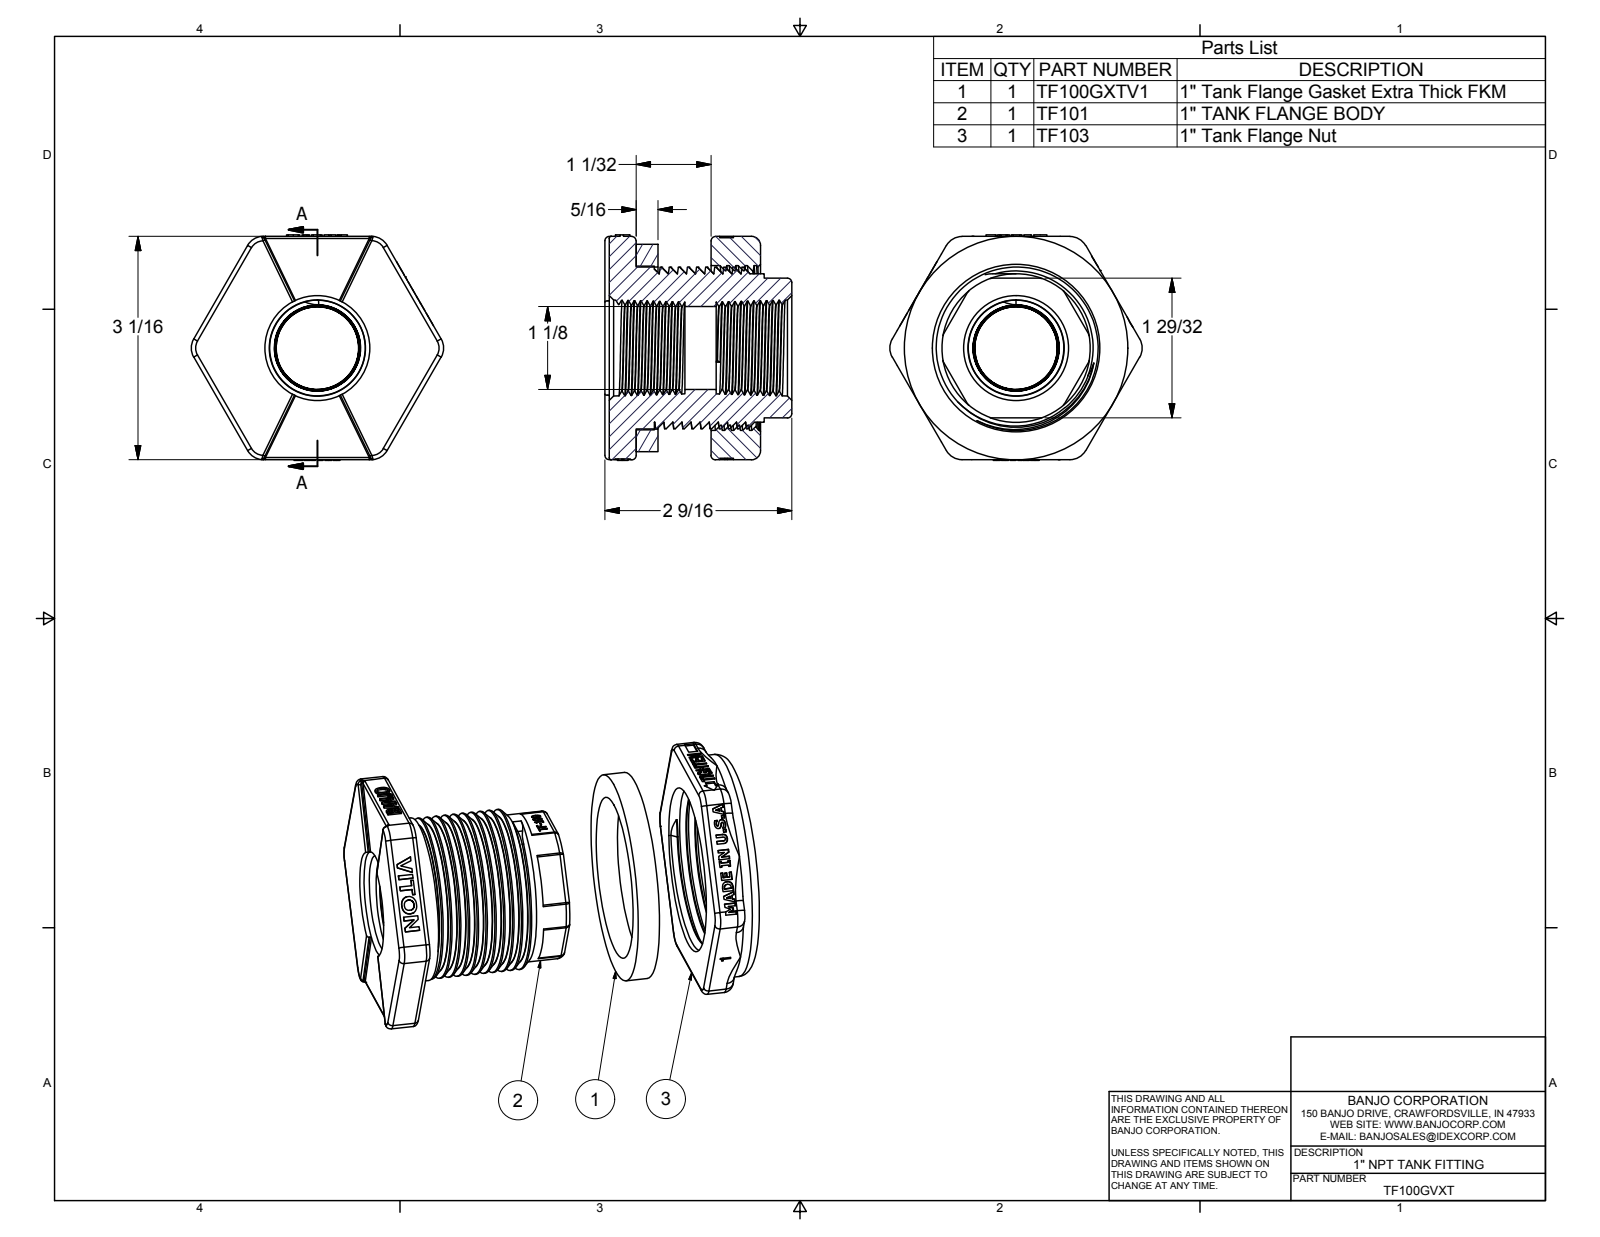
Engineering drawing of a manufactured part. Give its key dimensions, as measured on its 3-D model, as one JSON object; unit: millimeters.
{"part_name": "TF101; TF103X; TF103; TF100GXTV1 (+2 more)", "step_written_by": "Autodesk Inventor 2014 (AUTOMOTIVE_DESIGN)", "units": "millimeters", "bodies": {"solids": 8, "faces": 922, "planar": 543, "cylindrical": 99, "other": 280}, "overall_size": [88.08, 78.74, 65.28], "volume_mm3": 184536, "surface_area_mm2": 56572, "round_holes": [[28.96, 1], [53.85, 1], [56.52, 1], [57.53, 1]], "round_bosses_or_shafts": [[77.98, 1], [72.39, 1], [57.15, 1], [56.39, 1], [51.82, 1]], "partial_cylinders_radius": [[1.52, 28], [0.76, 6], [1.59, 6], [3.17, 6], [6.35, 6], [0.38, 4], [10, 1], [12.7, 1]], "face_to_face_distances": [10.92, 18.54, 37.08, 26.16, 54.36, 7.62, 77.98, 43.44, 35.82, 17.28]}
